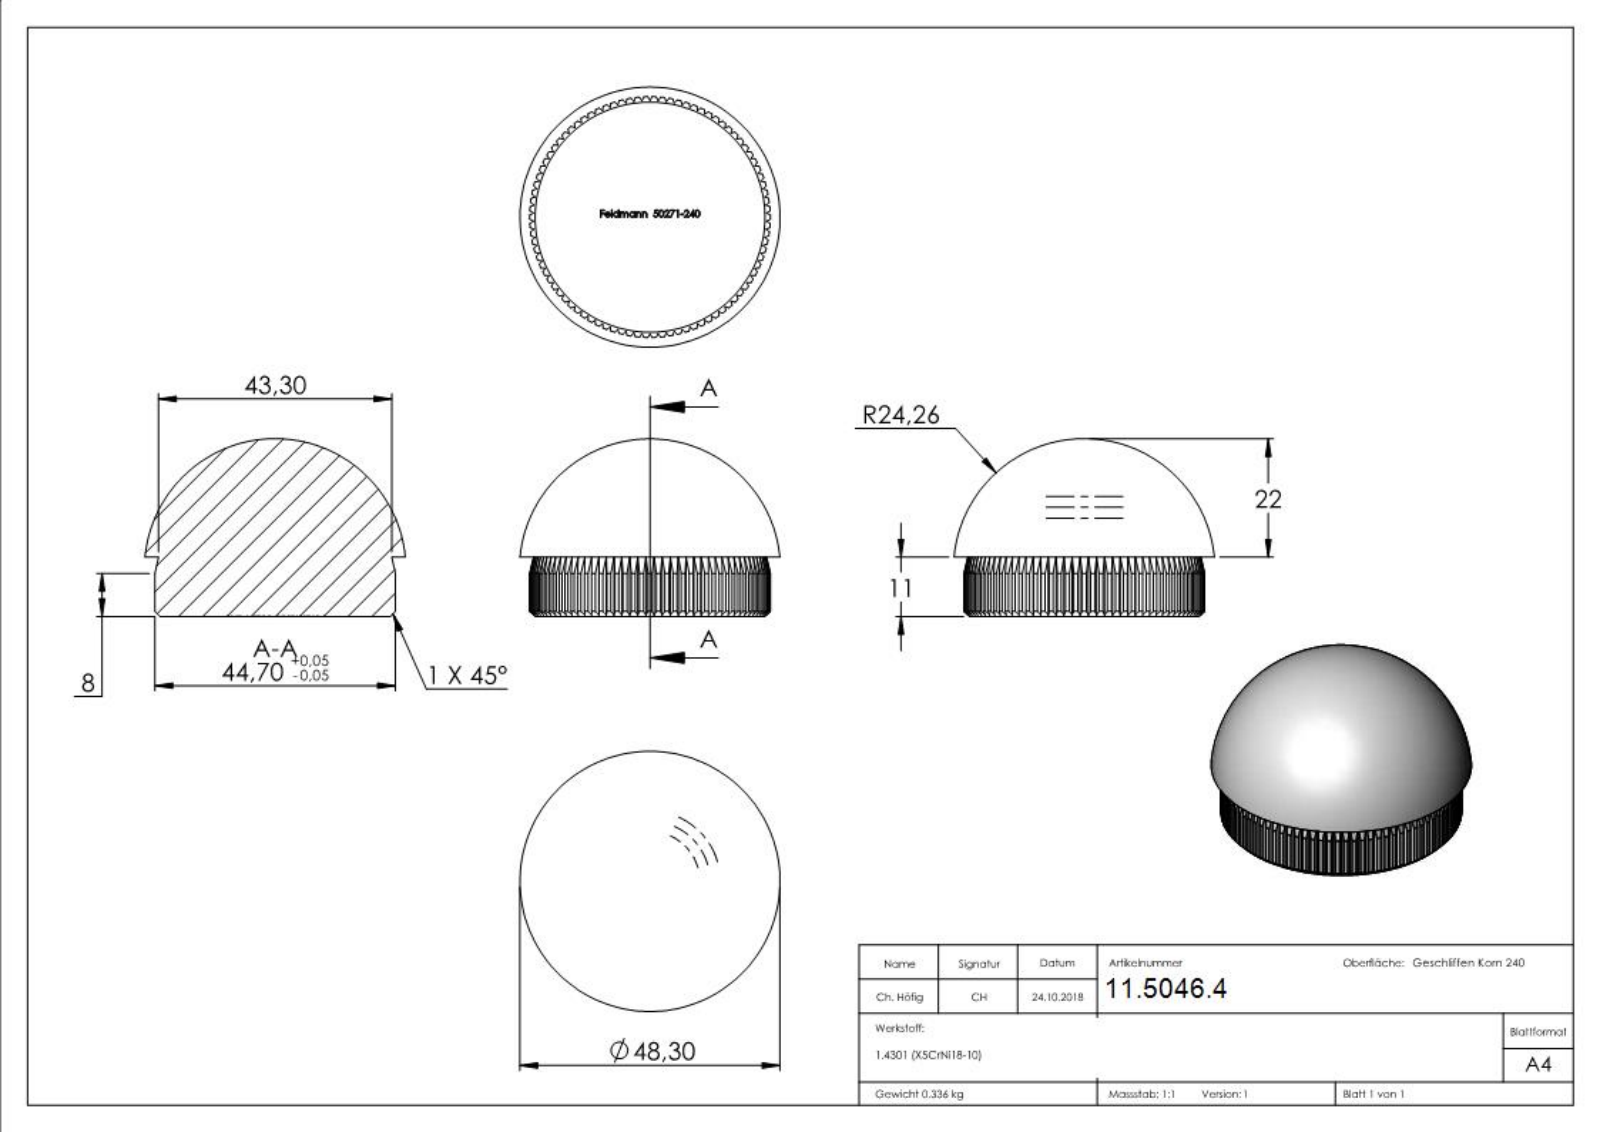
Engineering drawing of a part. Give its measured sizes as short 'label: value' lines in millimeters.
name: 50271-240
written by: SolidWorks 2015 (CONFIG_CONTROL_DESIGN)
unit: mm
bodies: 1 solid, 584 faces (306 planar, 90 cylindrical, 188 other)
size: 48.3 × 48.3 × 33
volume: 42 565 mm³; area: 7 384 mm²
rounds: 1× R22.35
face distances: 21.64, 11, 21.65, 21.66, 21.68, 21.62, 10.9, 10.83, 10.82, 1.32
